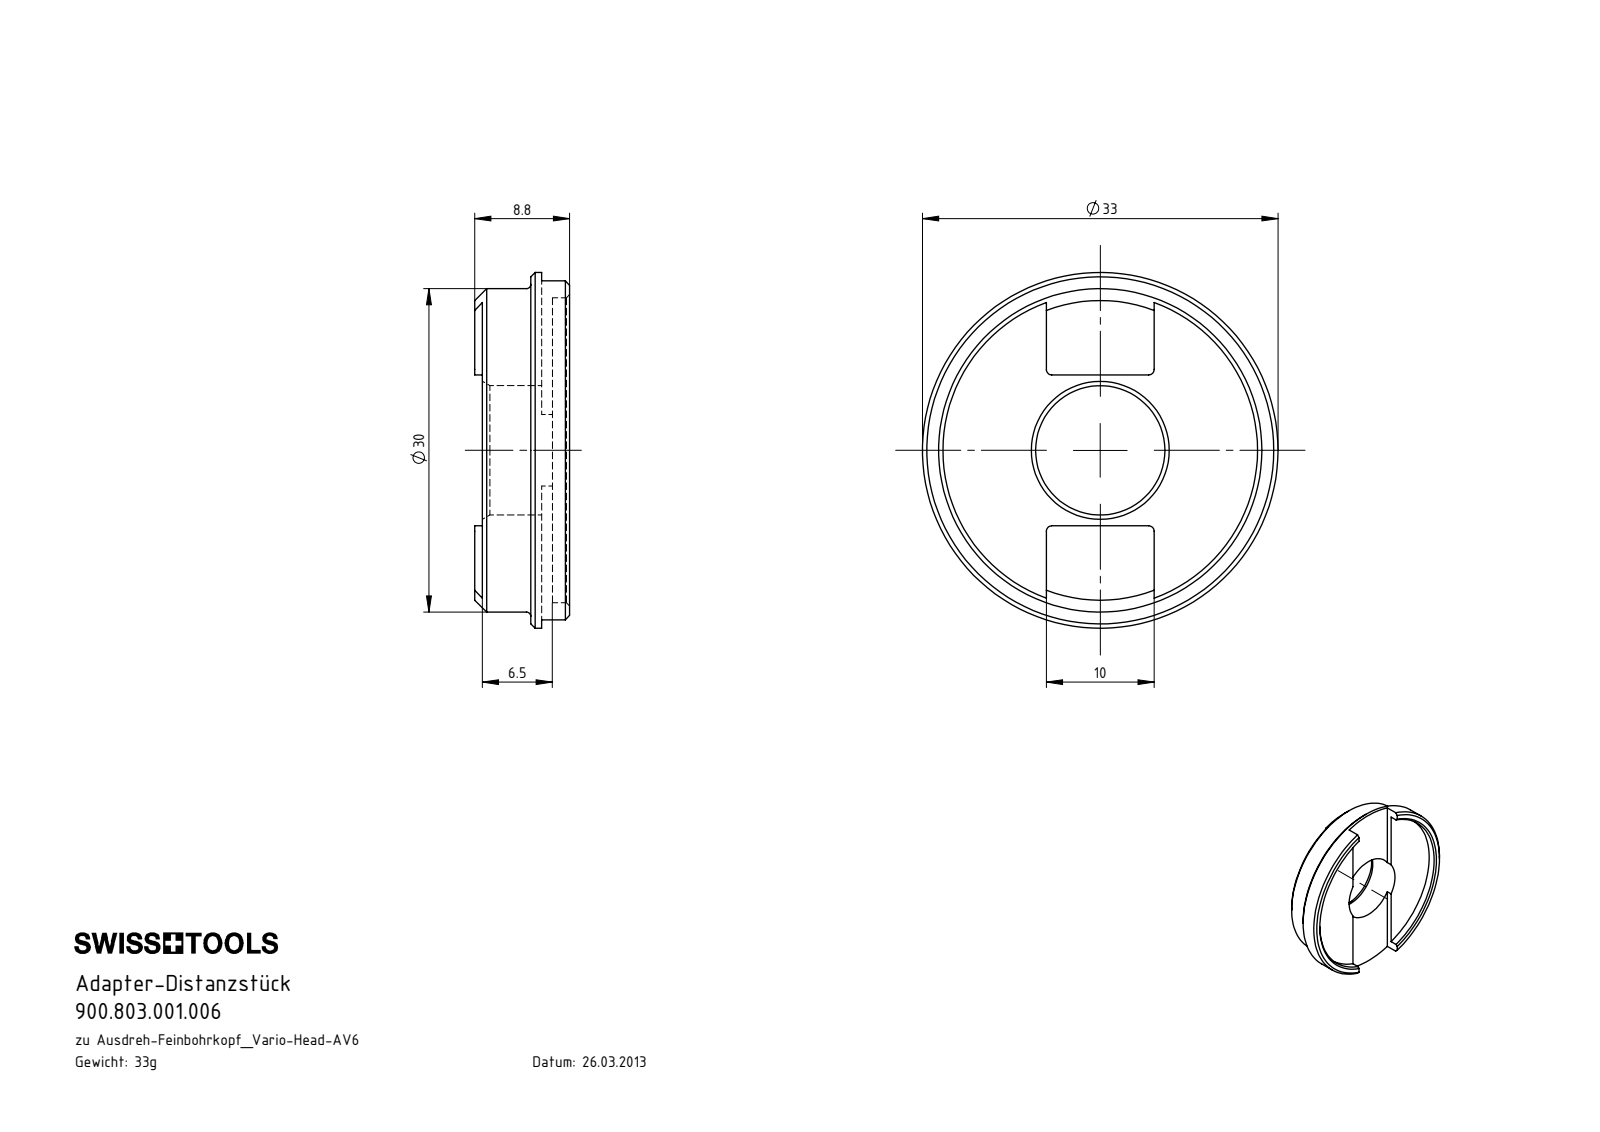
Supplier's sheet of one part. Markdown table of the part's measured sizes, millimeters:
| quantity | value |
| --- | --- |
| part name | 900.803.001.006 |
| STEP written by | SolidWorks 2017 (CONFIG_CONTROL_DESIGN) |
| units | millimeters |
| bodies | 1 solid, 47 faces (20 planar, 13 cylindrical, 14 other) |
| overall size | 33 × 33 × 8.8 |
| volume | 4 194 mm³ |
| surface area | 2 559 mm² |
| round holes (diameter × count) | 12 × 1, 30 × 1 |
| round bosses / shafts (diameter × count) | 33 × 1 |
| partial cylindrical surfaces (radius × count) | 0.5 × 4 |
| main face-to-face distances | 6.5, 1, 5.5, 0.7, 6.2, 7.2, 5.2, 4.5, 2, 8.8 |
